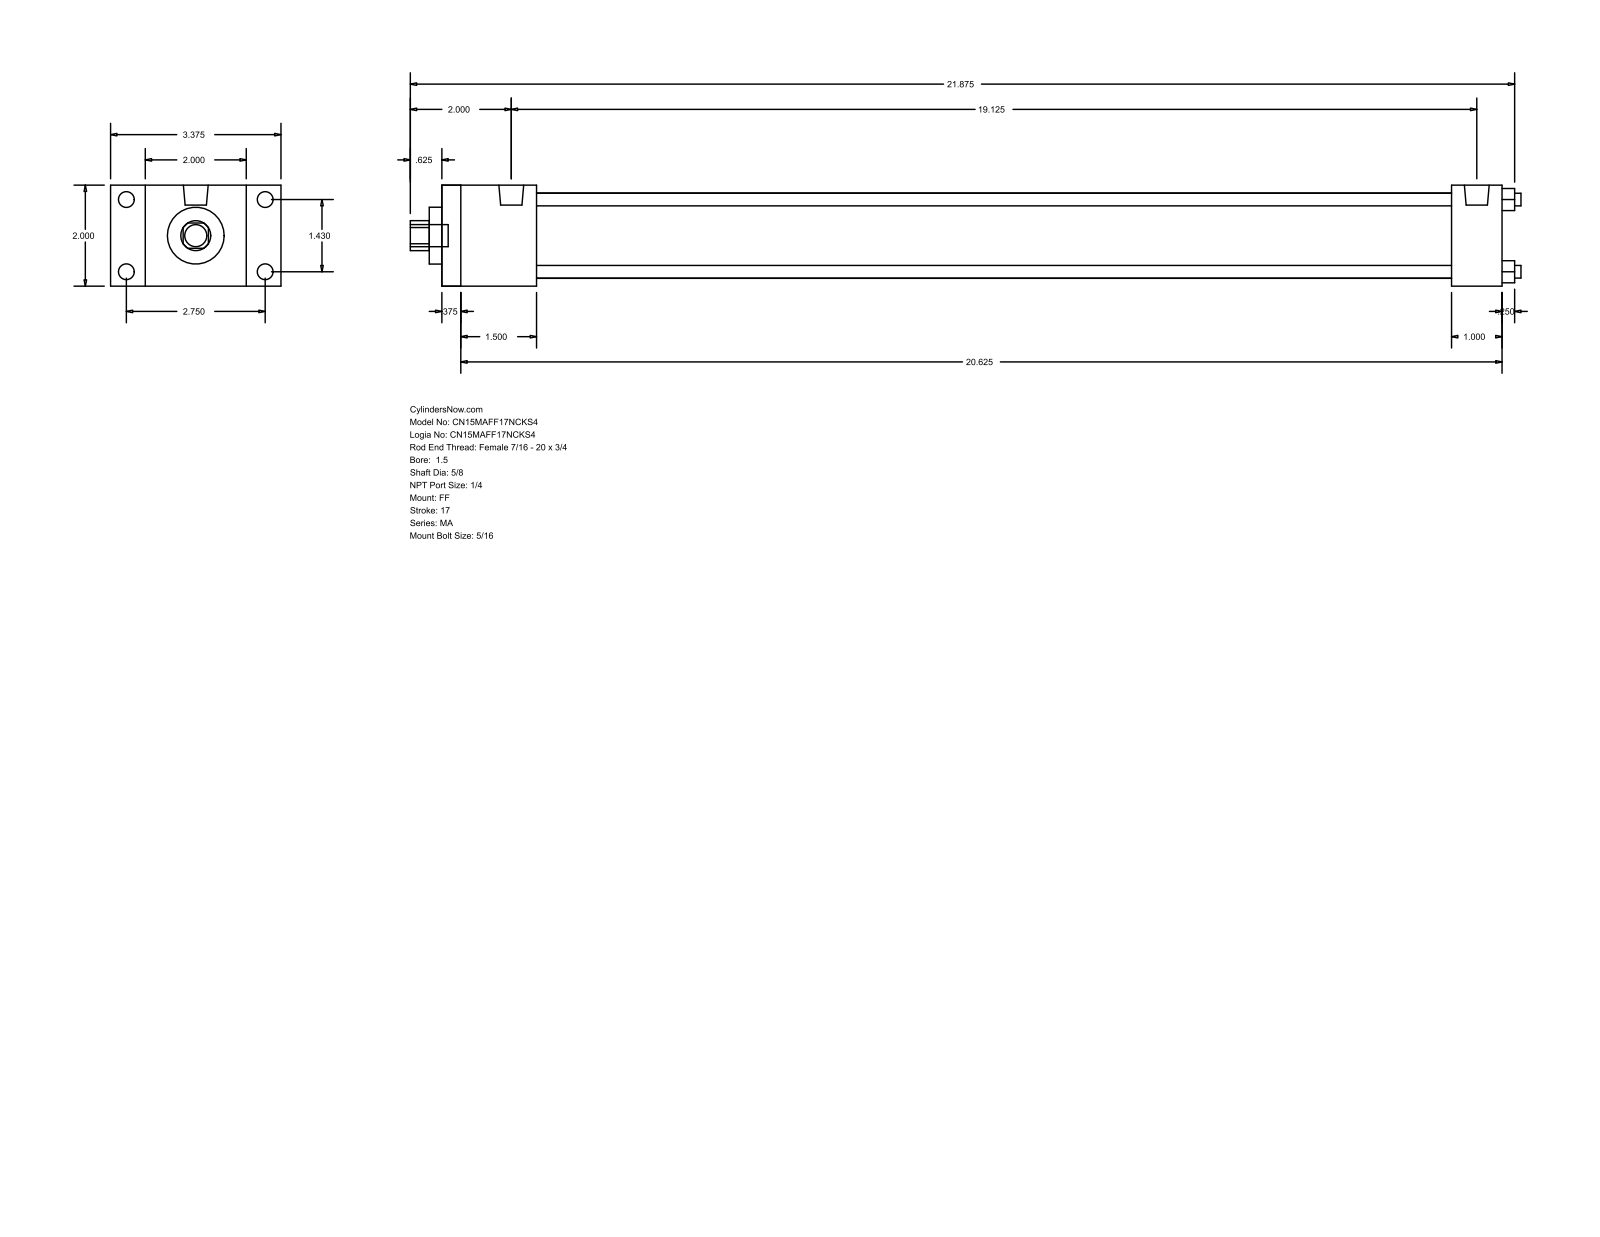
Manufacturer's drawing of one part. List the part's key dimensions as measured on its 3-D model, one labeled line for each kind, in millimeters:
Part name (STEP PRODUCT): MA_FF__0150_0.625
STEP written by: GSSL Pune (CONFIG_CONTROL_DESIGN)
Units: millimetres
Bodies: 0 solids, 92 faces (64 planar, 28 cylindrical, 0 other)
Overall size (bounding box): 558.8 × 85.72 × 50.8
Round holes (diameter × count): ⌀6.35 ×4, ⌀15.88 ×1, ⌀28.57 ×1, ⌀42.93 ×1
Round bosses / shafts (diameter × count): ⌀7.94 ×8, ⌀12.49 ×2, ⌀11.11 ×1
Partial cylindrical surfaces — rounded edges, fillets, slot ends (radius × count): R7.54 ×1
Main face-to-face distances: 50.8, 533.39, 9.52, 523.87, 47.62, 508, 38.1, 498.48, 460.38, 485.77
Hole centre spacings: 25.68, 36.32, 51.36
